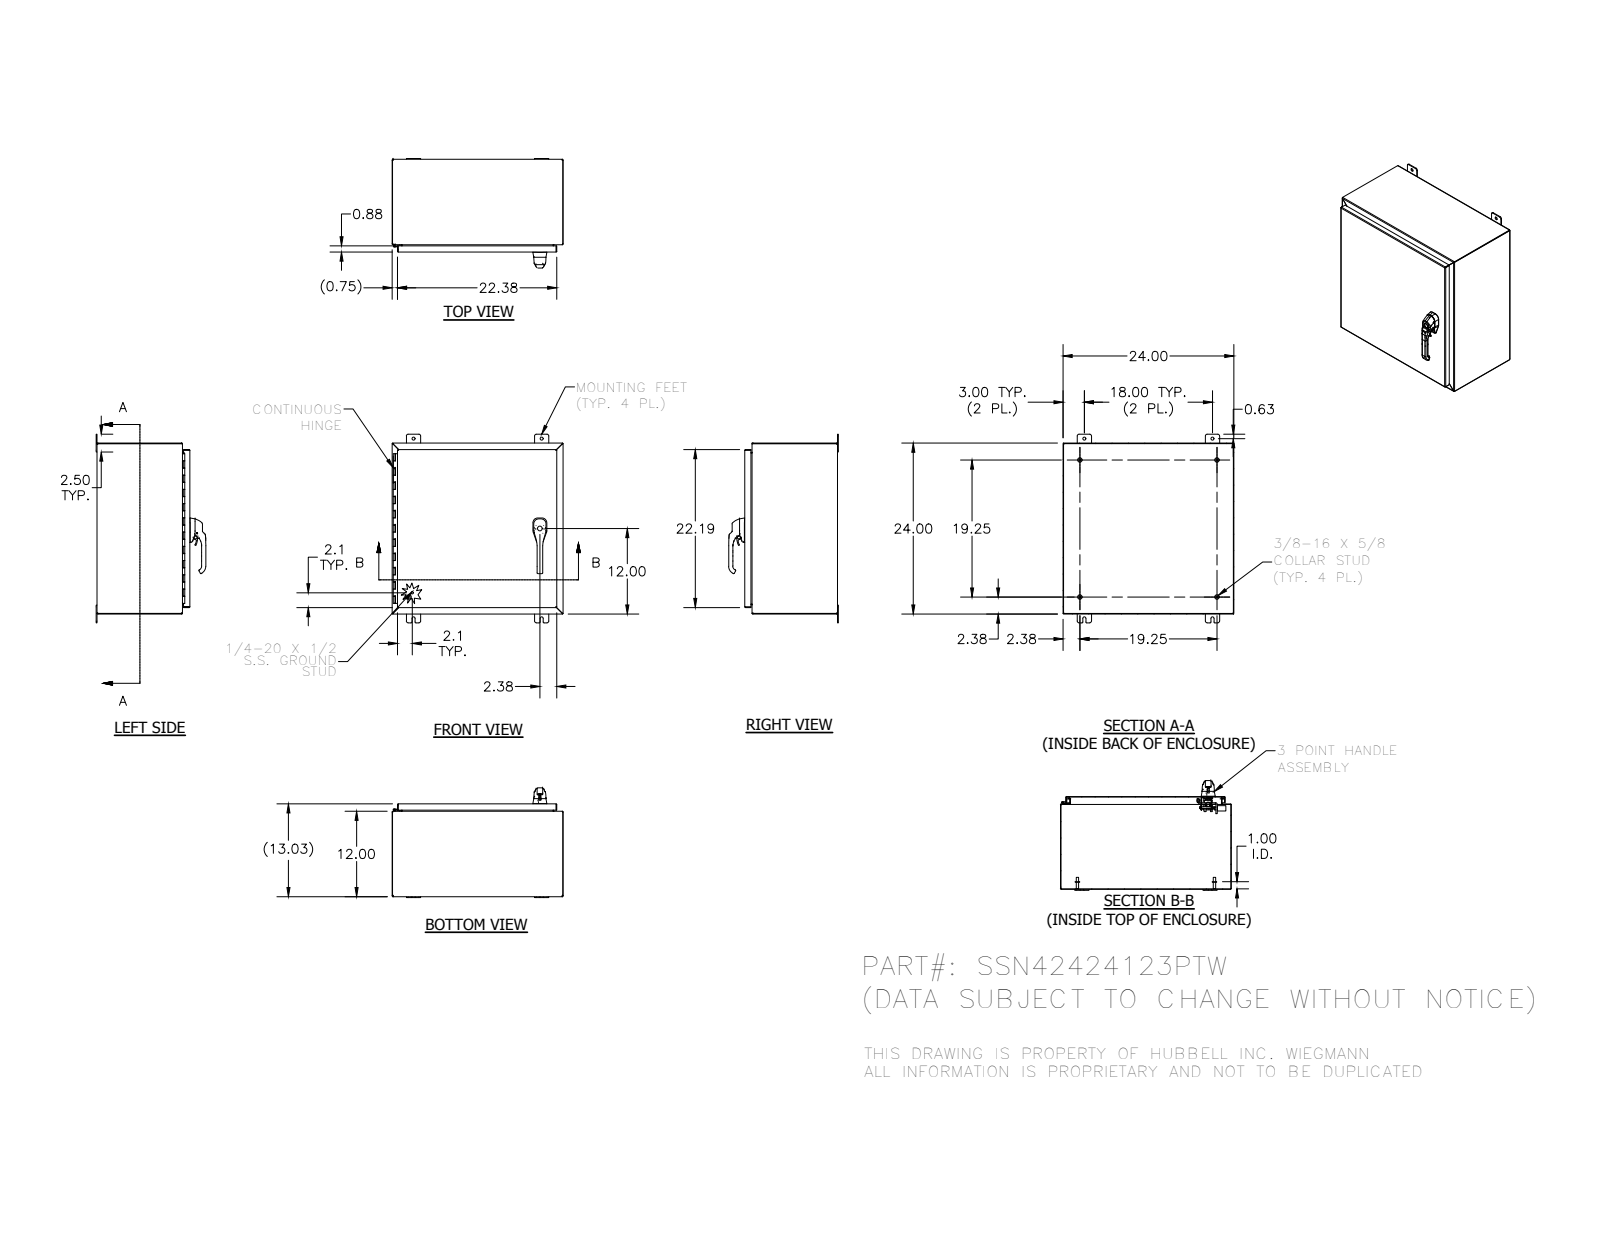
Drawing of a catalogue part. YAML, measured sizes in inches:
part_name: "328138T; 1091-BR11_AF0; PLASTIC-ROLLER-CAM_AF1; 1091-74-03 (+8 more)"
step_written_by: "SolidWorks 2014 (AUTOMOTIVE_DESIGN)"
units: inches
bodies: {solids: 56, faces: 3059, planar: 1014, cylindrical: 1260, other: 785}
overall_size: [26.5, 24, 15.408]
volume: 212.5
surface_area: 5495
round_holes:
  - {diameter: 0.262, count: 8}
  - {diameter: 0.187, count: 4}
  - {diameter: 0.438, count: 4}
  - {diameter: 0.213, count: 3}
  - {diameter: 0.281, count: 3}
  - {diameter: 0.241, count: 2}
  - {diameter: 0.25, count: 2}
  - {diameter: 0.252, count: 2}
  - {diameter: 0.315, count: 2}
  - {diameter: 0.4, count: 2}
  - {diameter: 0.402, count: 2}
  - {diameter: 0.413, count: 2}
round_bosses_or_shafts:
  - {diameter: 0.625, count: 4}
  - {diameter: 0.33, count: 4}
  - {diameter: 0.236, count: 3}
  - {diameter: 1, count: 2}
  - {diameter: 0.563, count: 2}
  - {diameter: 0.533, count: 2}
  - {diameter: 0.531, count: 2}
  - {diameter: 0.5, count: 2}
partial_cylinders:
  - {radius: 0.02, count: 172}
  - {radius: 0.012, count: 113}
  - {radius: 0.125, count: 26}
  - {radius: 0.031, count: 24}
  - {radius: 0.019, count: 21}
  - {radius: 0.105, count: 20}
  - {radius: 0.25, count: 20}
  - {radius: 0.025, count: 16}
face_to_face_distances: [0.074, 23.926, 12.959, 23.852, 24, 12.885, 13.033, 11.926, 1.033, 12]
hole_center_spacings: [0.38, 0.492, 0.76, 0.886, 14.428, 0.234, 0.258, 0.38]
